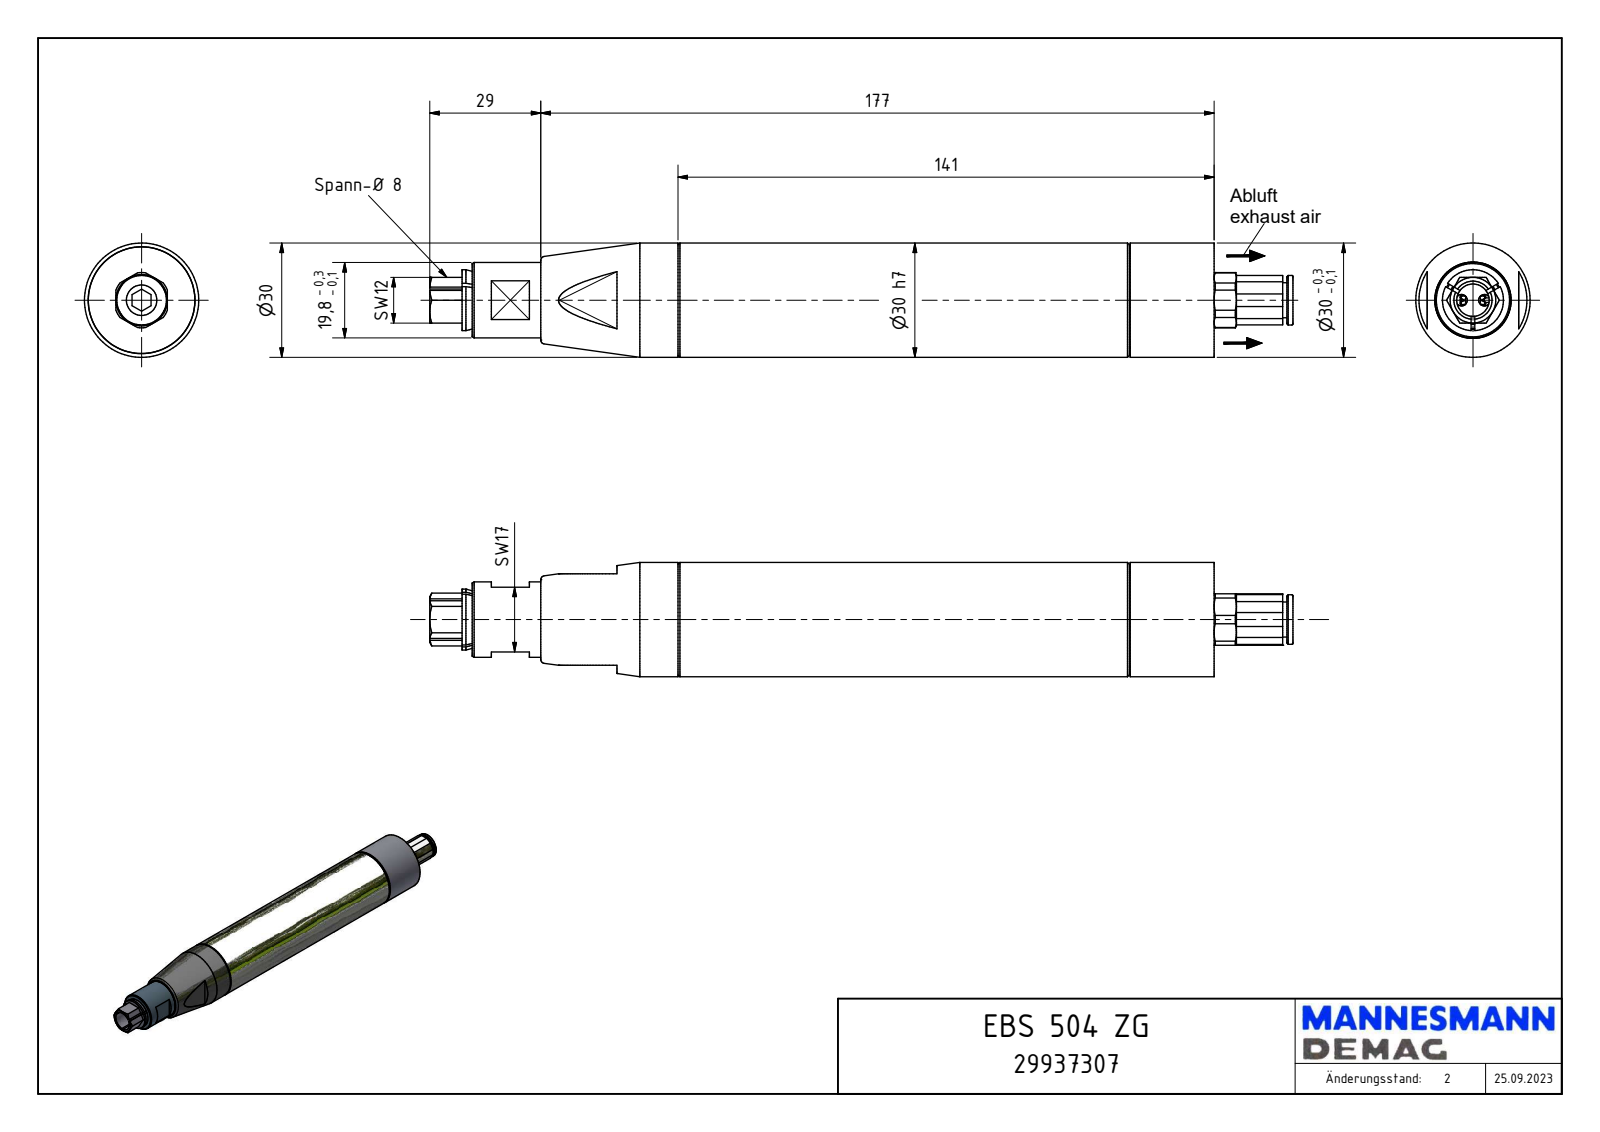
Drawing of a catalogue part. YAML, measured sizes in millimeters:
part_name: "EBS 504 ZG_29937307"
step_written_by: "Autodesk Inventor 2024 (AUTOMOTIVE_DESIGN)"
units: millimeters
bodies: {solids: 1, faces: 164, planar: 86, cylindrical: 41, other: 37}
overall_size: [226.61, 30, 30]
volume: 126718
surface_area: 22879
round_holes:
  - {diameter: 8, count: 1}
  - {diameter: 8.5, count: 1}
  - {diameter: 8.57, count: 1}
  - {diameter: 10, count: 1}
  - {diameter: 12.1, count: 1}
  - {diameter: 12.5, count: 1}
  - {diameter: 12.7, count: 1}
round_bosses_or_shafts:
  - {diameter: 30, count: 1}
  - {diameter: 28, count: 1}
  - {diameter: 19.8, count: 1}
  - {diameter: 16, count: 1}
  - {diameter: 13, count: 1}
  - {diameter: 12, count: 1}
  - {diameter: 11.5, count: 1}
  - {diameter: 9.2, count: 1}
partial_cylinders:
  - {radius: 22.5, count: 3}
  - {radius: 6.75, count: 1}
  - {radius: 7.25, count: 1}
face_to_face_distances: [12.5, 20.5, 0.5, 3.5, 6.25, 7.25, 24, 12, 194.75, 1]
